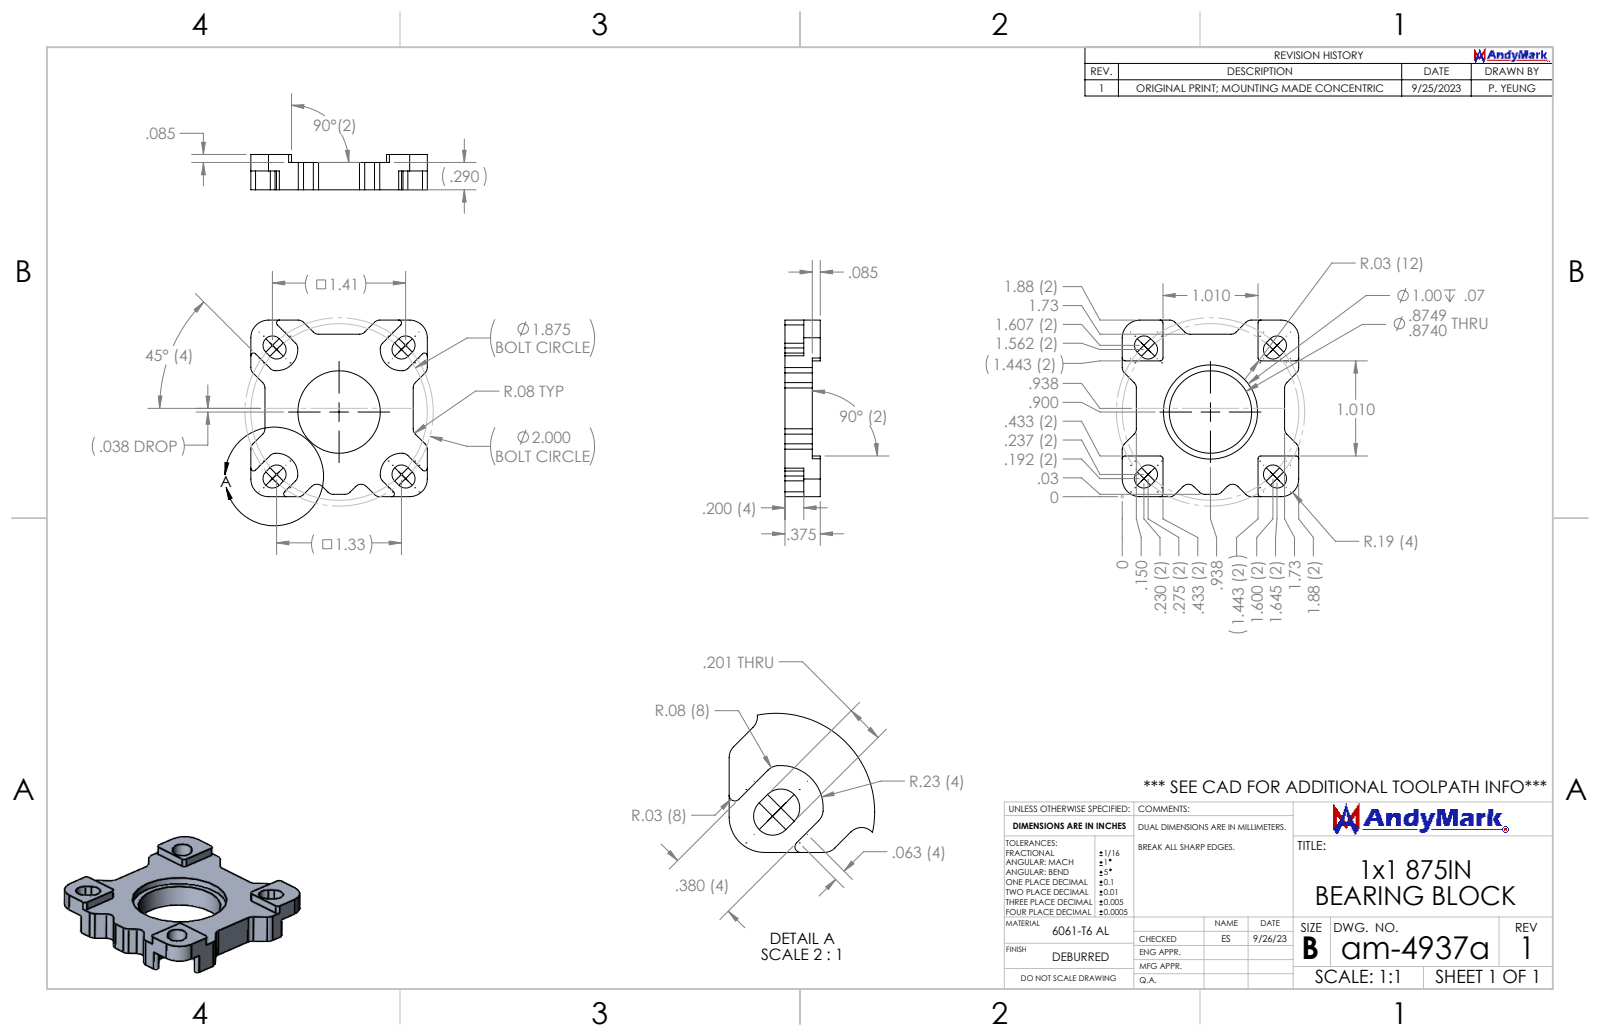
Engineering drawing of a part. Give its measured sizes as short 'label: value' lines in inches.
name: am-4937a 1IN x 1IN 875IN Bearing Block
written by: SolidWorks 2022 (AUTOMOTIVE_DESIGN)
unit: in
bodies: 1 solid, 133 faces (57 planar, 76 cylindrical, 0 other)
size: 1.875 × 1.875 × 0.375
volume: 0.609 in³; area: 9.23 in²
holes: 1× ⌀0.875, 1× ⌀1
rounds: 26× R0.08, 20× R0.03, 8× R0.101, 4× R0.187, 4× R0.225
face distances: 0.29, 0.2, 0.09, 0.375, 0.175, 0.085, 0.15, 1.443, 1.725, 1.293
